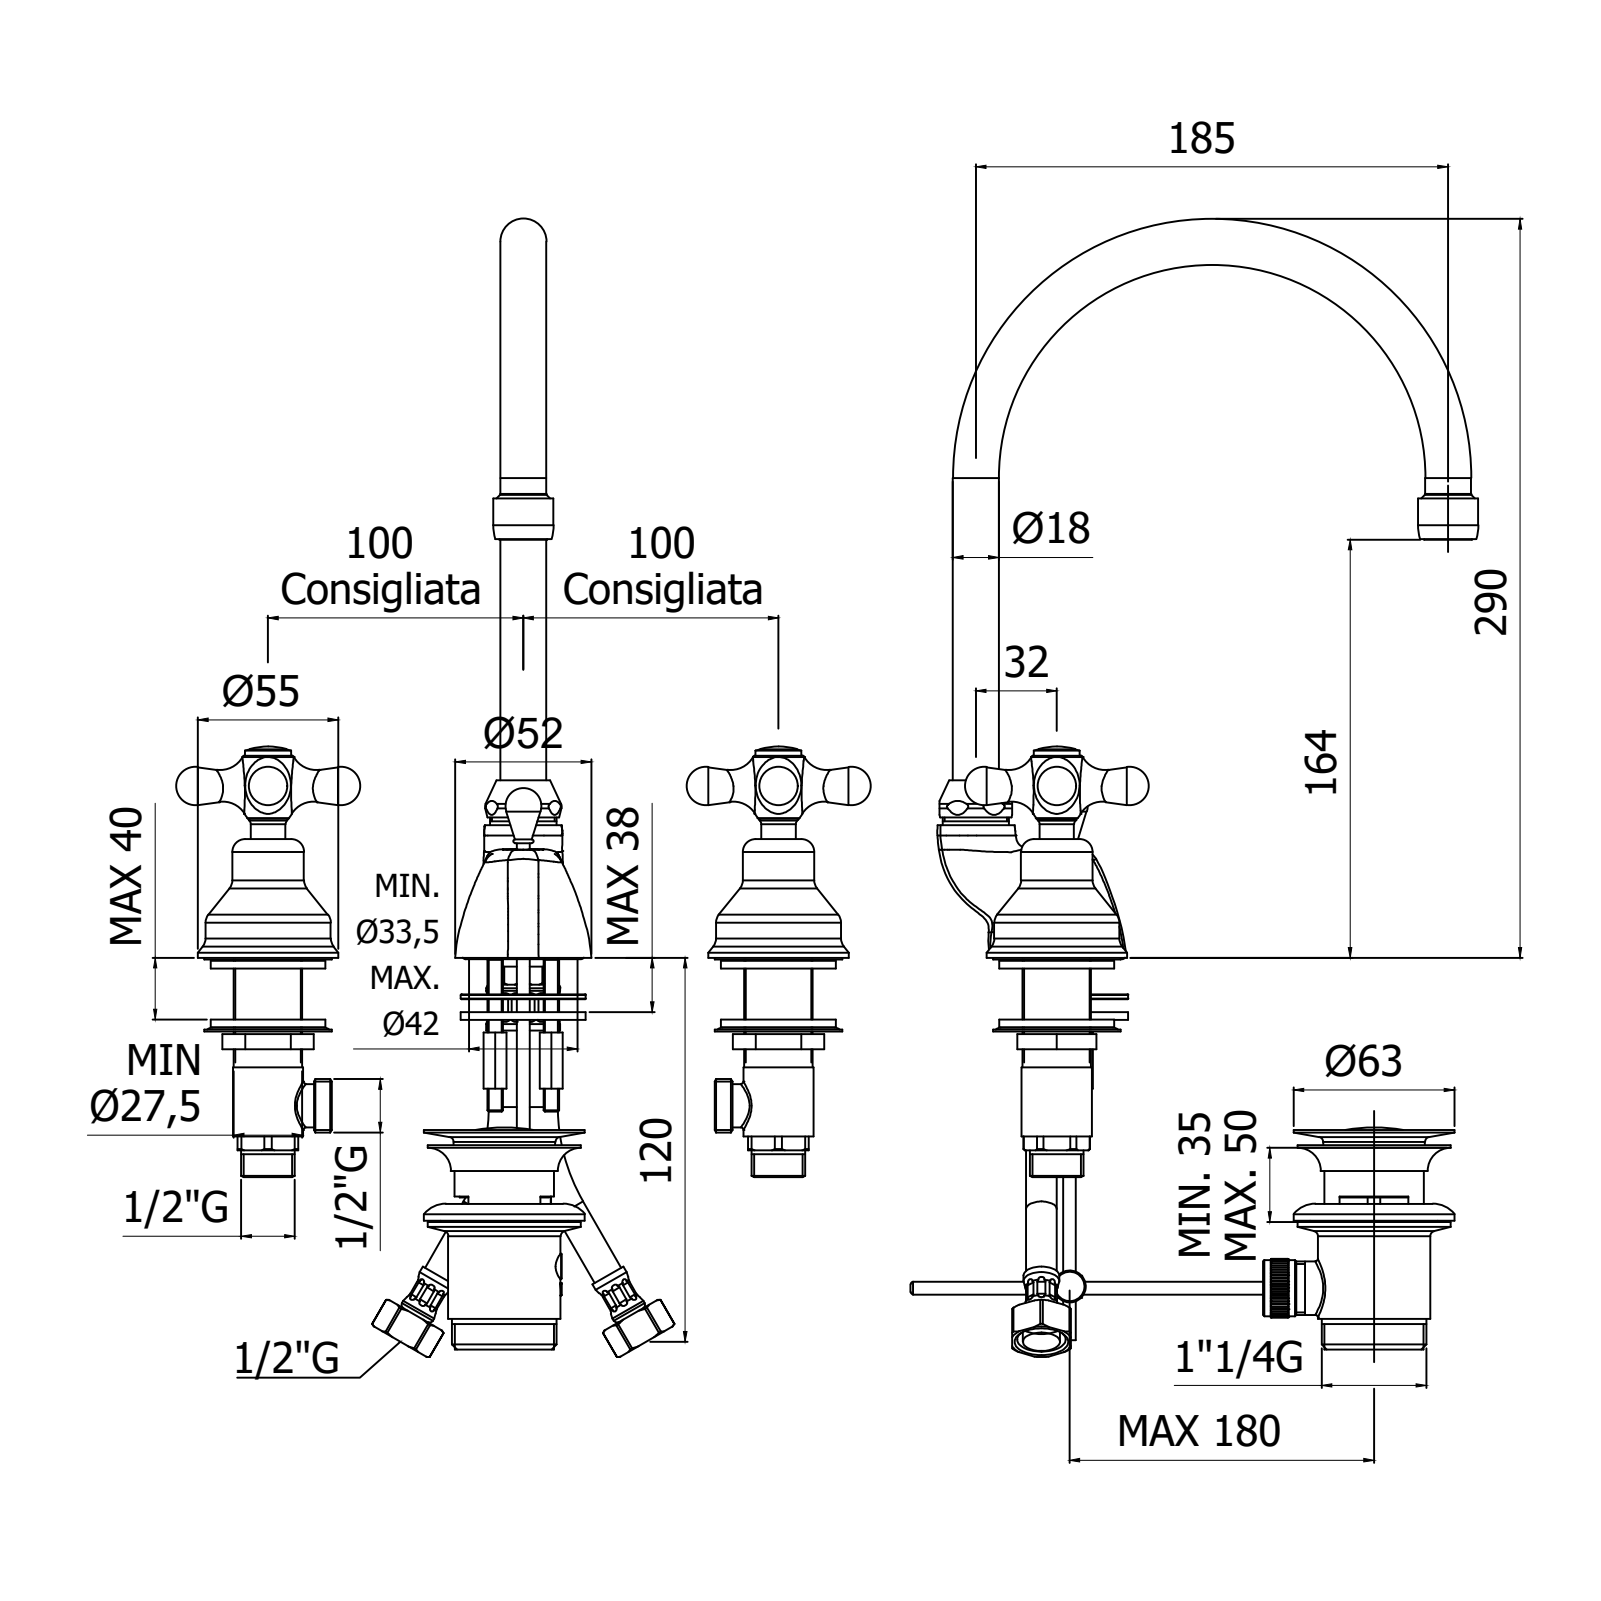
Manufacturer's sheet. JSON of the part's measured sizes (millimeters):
{"part_name": "IRV057CR", "step_written_by": "CREO PARAMETRIC BY PTC INC, 2020044 (CONFIG_CONTROL_DESIGN)", "units": "millimeters", "bodies": {"solids": 11, "faces": 2250, "planar": 1626, "cylindrical": 272, "other": 352}, "overall_size": [290, 272, 211.88], "volume_mm3": 194833, "surface_area_mm2": 136262, "round_holes": [[4.5, 2], [8, 2], [8.8, 2], [9, 2], [10.3, 2], [11, 2], [16, 2], [16.2, 2], [16.3, 2], [19, 2], [25.7, 2], [45, 2]], "round_bosses_or_shafts": [[18, 4], [21.4, 3], [5, 3], [55, 2], [49, 2], [29.5, 2], [28, 2], [26.8, 2]], "partial_cylinders_radius": [[0.1, 34], [0.5, 4], [1, 4], [1.5, 4], [7.5, 4], [2.5, 2], [5, 2], [9.4, 2]], "face_to_face_distances": [1, 3, 6, 5, 2, 10, 4, 14, 44, 17], "hole_center_spacings": [9.6, 13.31, 26.77, 92.69, 100, 100.12, 104.9, 107.67]}
